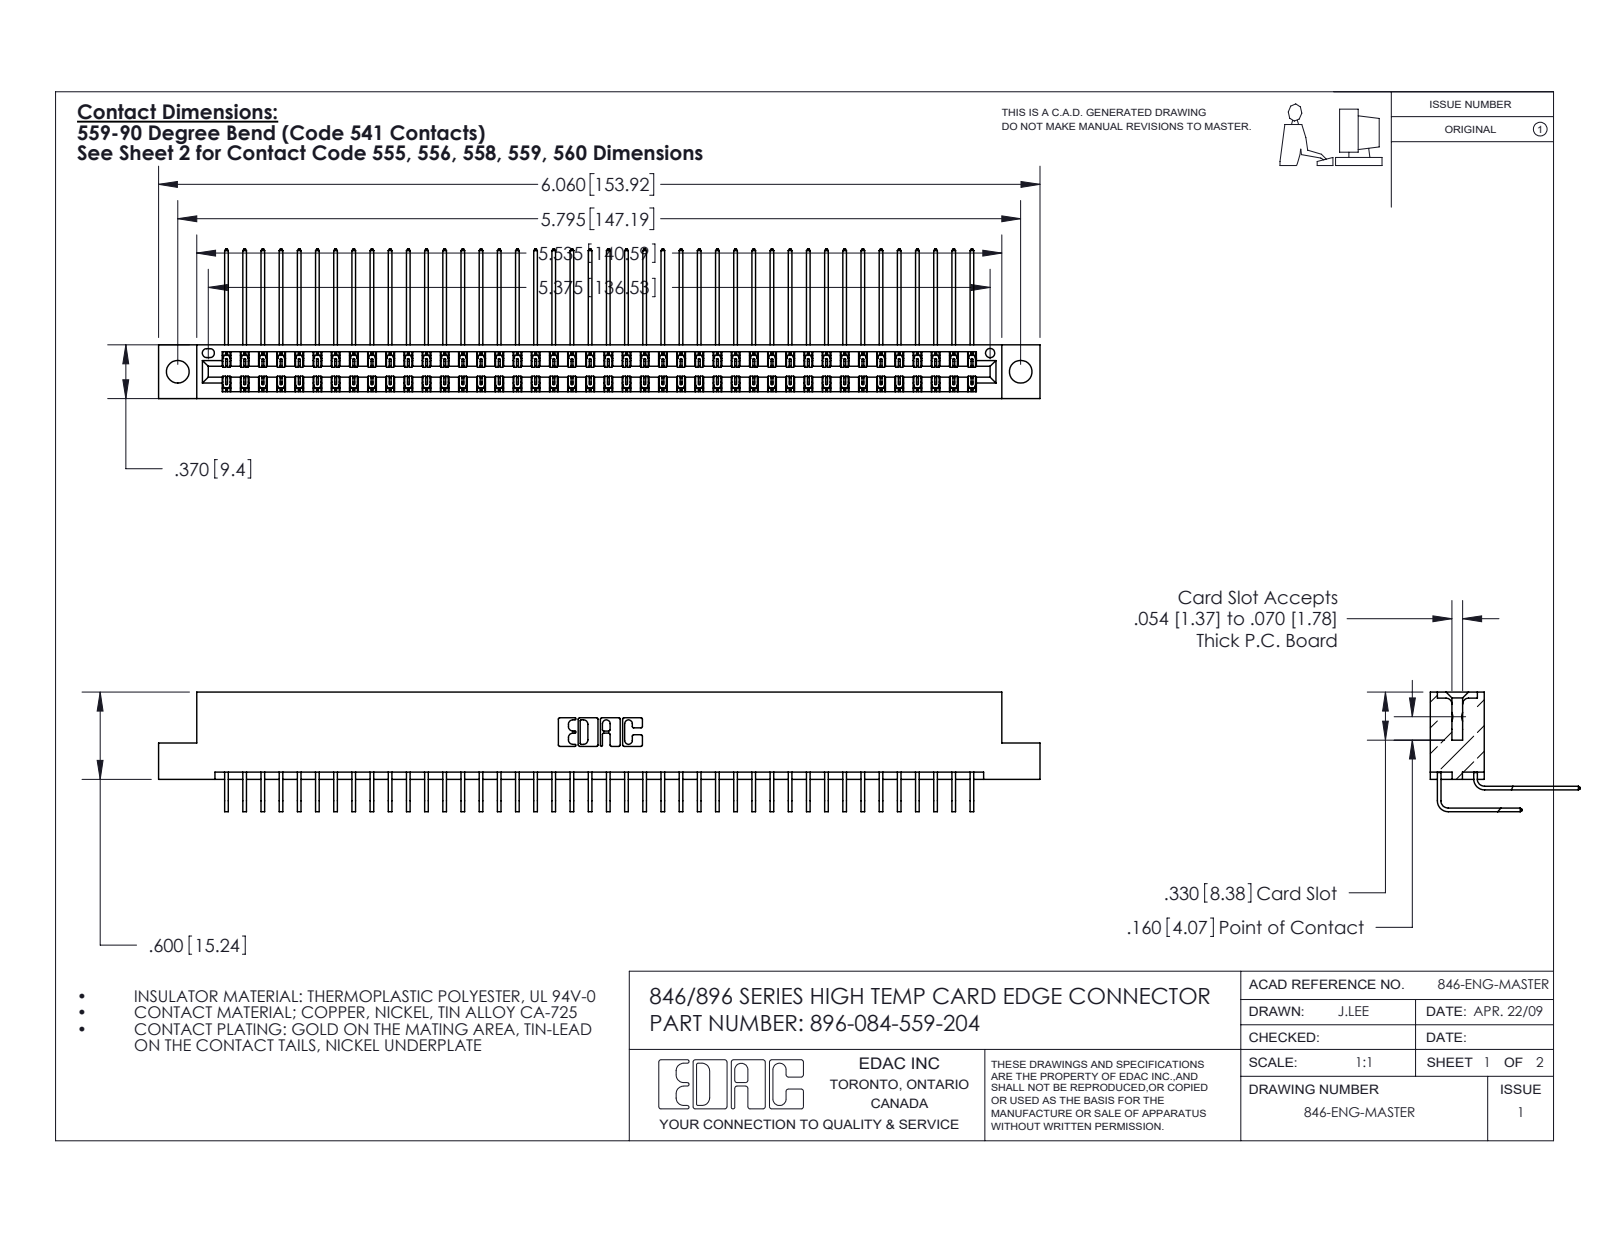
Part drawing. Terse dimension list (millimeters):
name: 345-292-001_558 559 Tail - 1; 346 Part_Flush Mounting Lugs - 0.156 Dia-TH; 396-084-559-204; 345-292-001_559 Tail - 2
written by: SolidWorks 2016 (CONFIG_CONTROL_DESIGN)
unit: mm
bodies: 85 solids, 4658 faces (3184 planar, 1474 cylindrical, 0 other)
size: 153.9 × 26.2 × 20.9
volume: 15 400 mm³; area: 23 320 mm²
holes: 2× ⌀4, 1× ⌀1.6
rounds: 126× R0.2, 22× R0.3, 6× R0.2, 6× R0.8, 3× R0.7, 2× R0.4, 2× R0.6, 2× R0.6
face distances: 1.2, 8.2, 0.6, 9.4, 6.4, 1.8, 7.6, 7, 3.8, 5.6
hole spacings: 6.2, 141.9, 147.2
